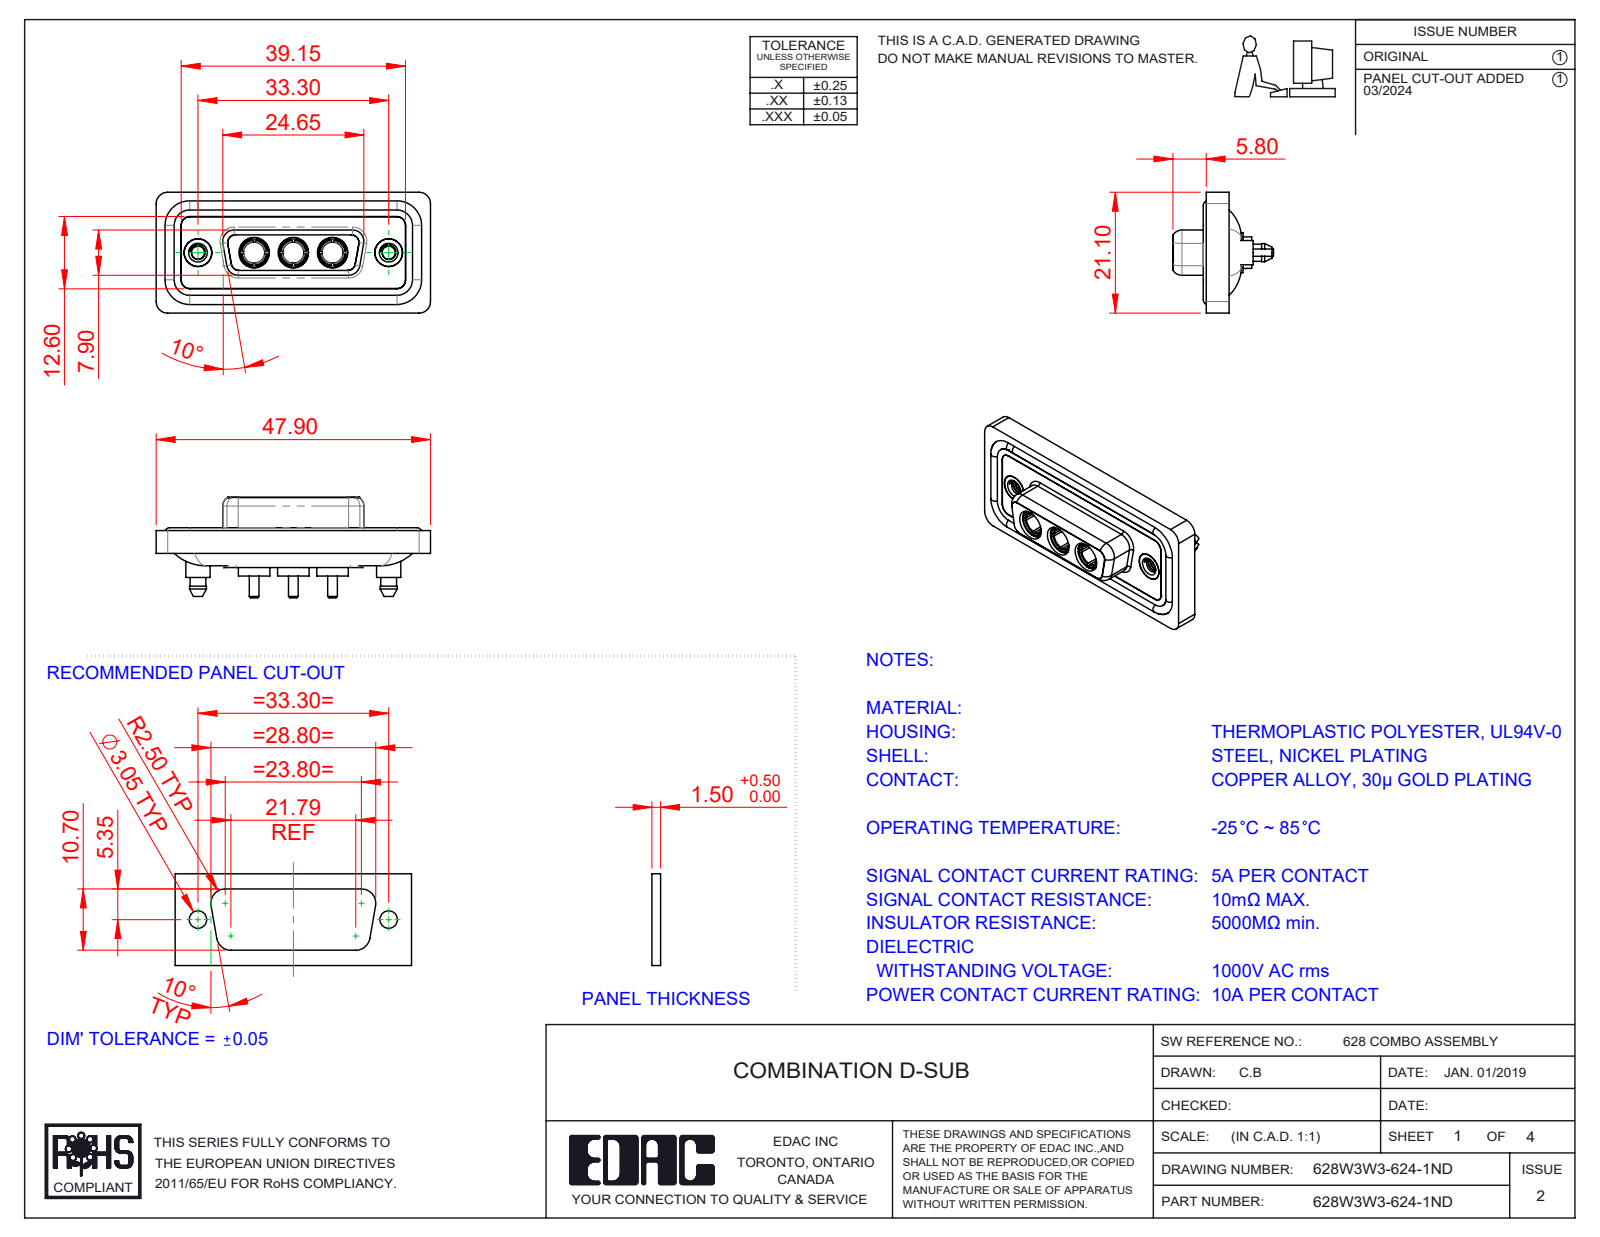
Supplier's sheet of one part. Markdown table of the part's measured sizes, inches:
| quantity | value |
| --- | --- |
| part name | 628Combo Waterproof Housing_15 Contacts; 628Combo Threaded Boardlock_D; 628Combo Shell Rear_15 Contacts; 628Combo Housing_3W3 (+3 more) |
| STEP written by | SolidWorks 2023 (CONFIG_CONTROL_DESIGN) |
| units | inches |
| bodies | 13 solids, 674 faces (208 planar, 305 cylindrical, 161 other) |
| overall size | 1.886 × 0.831 × 0.691 |
| volume | 0.373 in³ |
| surface area | 15.56 in² |
| round holes (diameter × count) | 0.191 × 5, 0.146 × 3, 0.209 × 3, 0.089 × 2, 0.157 × 2, 0.159 × 2, 0.197 × 2 |
| round bosses / shafts (diameter × count) | 0.063 × 4, 0.217 × 3, 0.205 × 3, 0.195 × 3, 0.187 × 3, 0.148 × 3, 0.067 × 3, 0.213 × 2 |
| partial cylindrical surfaces (radius × count) | 0.059 × 24, 0.079 × 20, 0.053 × 12, 0.063 × 10, 0.01 × 4, 0.02 × 4, 0.024 × 4, 0.026 × 4 |
| main face-to-face distances | 0.016, 0.071, 0.063, 0.02, 0.293, 0.043, 0.114, 0.222, 0.278, 0.059 |
| hole center spacings | 0.27, 0.386, 0.656, 0.925, 0.539, 1.311 |
